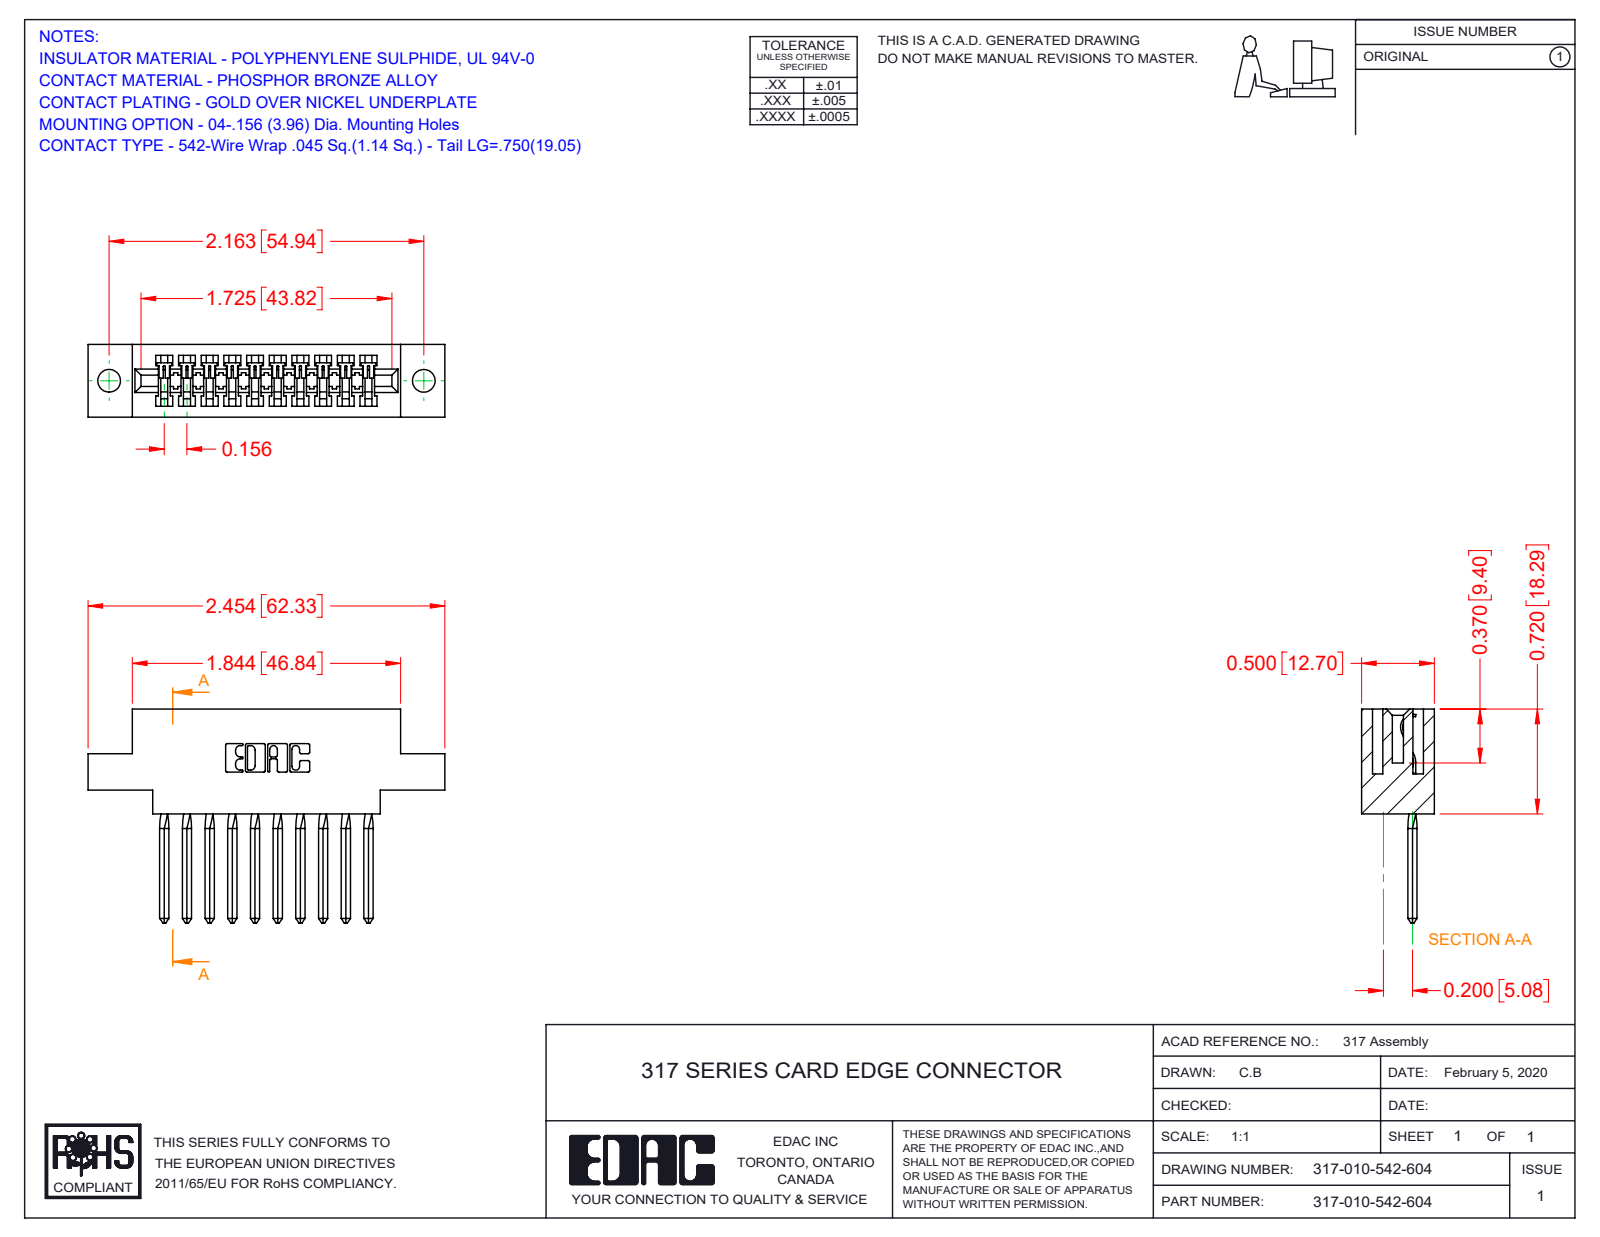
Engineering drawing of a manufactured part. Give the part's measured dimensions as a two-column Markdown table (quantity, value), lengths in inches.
| quantity | value |
| --- | --- |
| part name | 317-290-003_542; 317-010-542-604; 317 Part_.156 Dia - TH |
| STEP written by | SolidWorks 2016 (CONFIG_CONTROL_DESIGN) |
| units | inches |
| bodies | 11 solids, 852 faces (698 planar, 114 cylindrical, 40 other) |
| overall size | 2.454 × 1.47 × 0.5 |
| volume | 0.53 in³ |
| surface area | 15.02 in² |
| round holes (diameter × count) | 0.156 × 2 |
| partial cylindrical surfaces (radius × count) | 0.01 × 22, 0.006 × 20, 0.007 × 6, 0.031 × 6, 0.026 × 3, 0.074 × 1, 0.089 × 1, 0.1 × 1 |
| main face-to-face distances | 0.5, 0.075, 0.425, 0.11, 0.065, 0.22, 0.35, 0.331, 0.156, 0.116 |
| hole center spacings | 2.163 |
